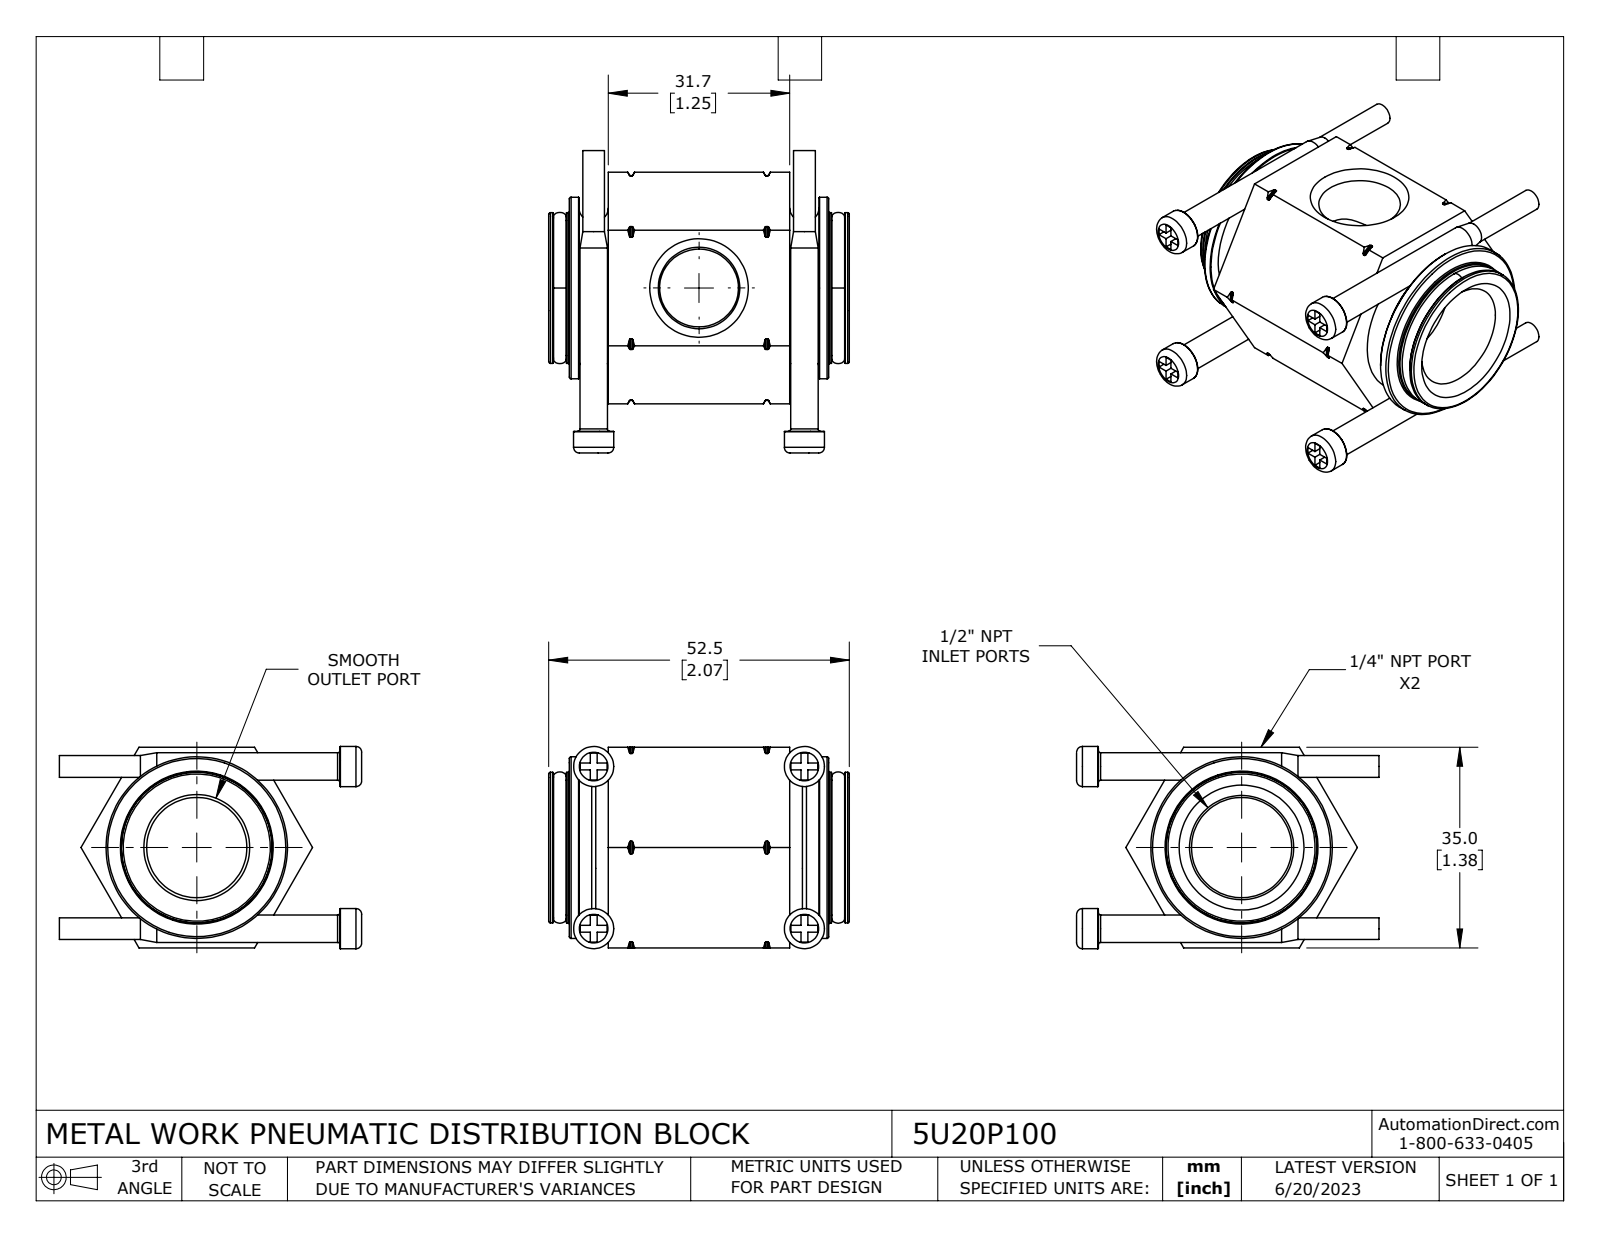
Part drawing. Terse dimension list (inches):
name: 5U20P100
written by: SolidWorks 2021 (CONFIG_CONTROL_DESIGN)
unit: in
bodies: 7 solids, 288 faces (82 planar, 60 cylindrical, 146 other)
size: 2.079 × 2.067 × 1.39
volume: 1.972 in³; area: 25.01 in²
holes: 1× ⌀0.689
bosses: 4× ⌀0.276, 4× ⌀0.189, 4× ⌀0.15, 1× ⌀1.248, 1× ⌀1.035, 1× ⌀0.925, 1× ⌀0.917
rounds: 1× R0.772
face distances: 1.378, 1.248, 1.449, 0.409, 1.657, 0.268, 1.516, 0.142, 1.925, 0.067
